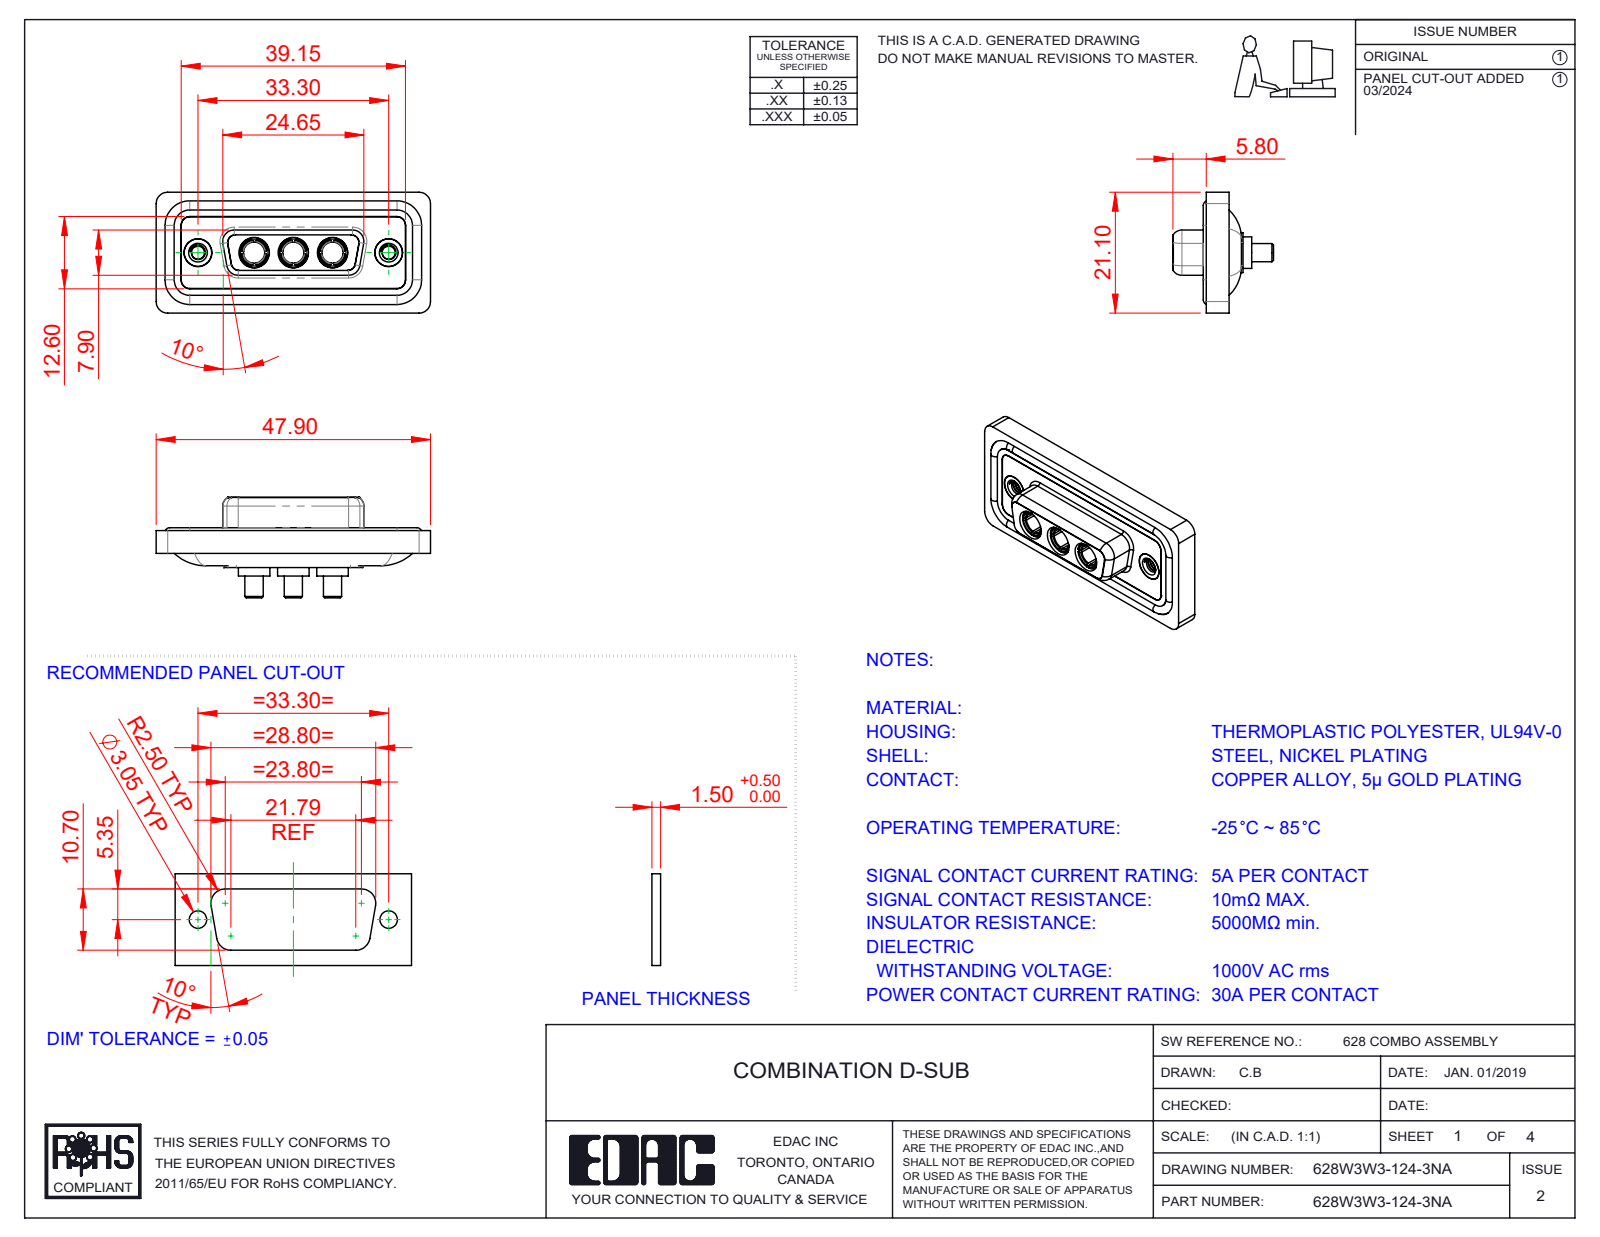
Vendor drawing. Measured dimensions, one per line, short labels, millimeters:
name: 628Combo Housing_3W3; 628Combo Shell Front_15 Contacts; 628W3W3-124-3NA; 628Combo Waterproof Housing_15 Contacts (+3 more)
written by: SolidWorks 2023 (CONFIG_CONTROL_DESIGN)
unit: mm
bodies: 13 solids, 606 faces (192 planar, 259 cylindrical, 155 other)
size: 47.9 × 21.1 × 17.55
volume: 6 049 mm³; area: 9 750 mm²
holes: 5× ⌀4.85, 3× ⌀3.7, 3× ⌀5.3, 2× ⌀2.26, 2× ⌀4, 2× ⌀4.05, 2× ⌀5
bosses: 4× ⌀1.6, 3× ⌀5.5, 3× ⌀5.2, 3× ⌀4.96, 3× ⌀4.75, 3× ⌀3.75, 3× ⌀3.2, 2× ⌀4.95
rounds: 22× R1.5, 20× R2, 12× R1.35, 8× R1.6, 4× R0.25, 4× R0.5, 4× R0.6, 4× R0.65
face distances: 0.4, 1.8, 1.6, 0.5, 7.45, 1.1, 2.9, 5.65, 7.05, 6.6
hole spacings: 6.85, 9.8, 16.65, 23.5, 13.7, 33.3
